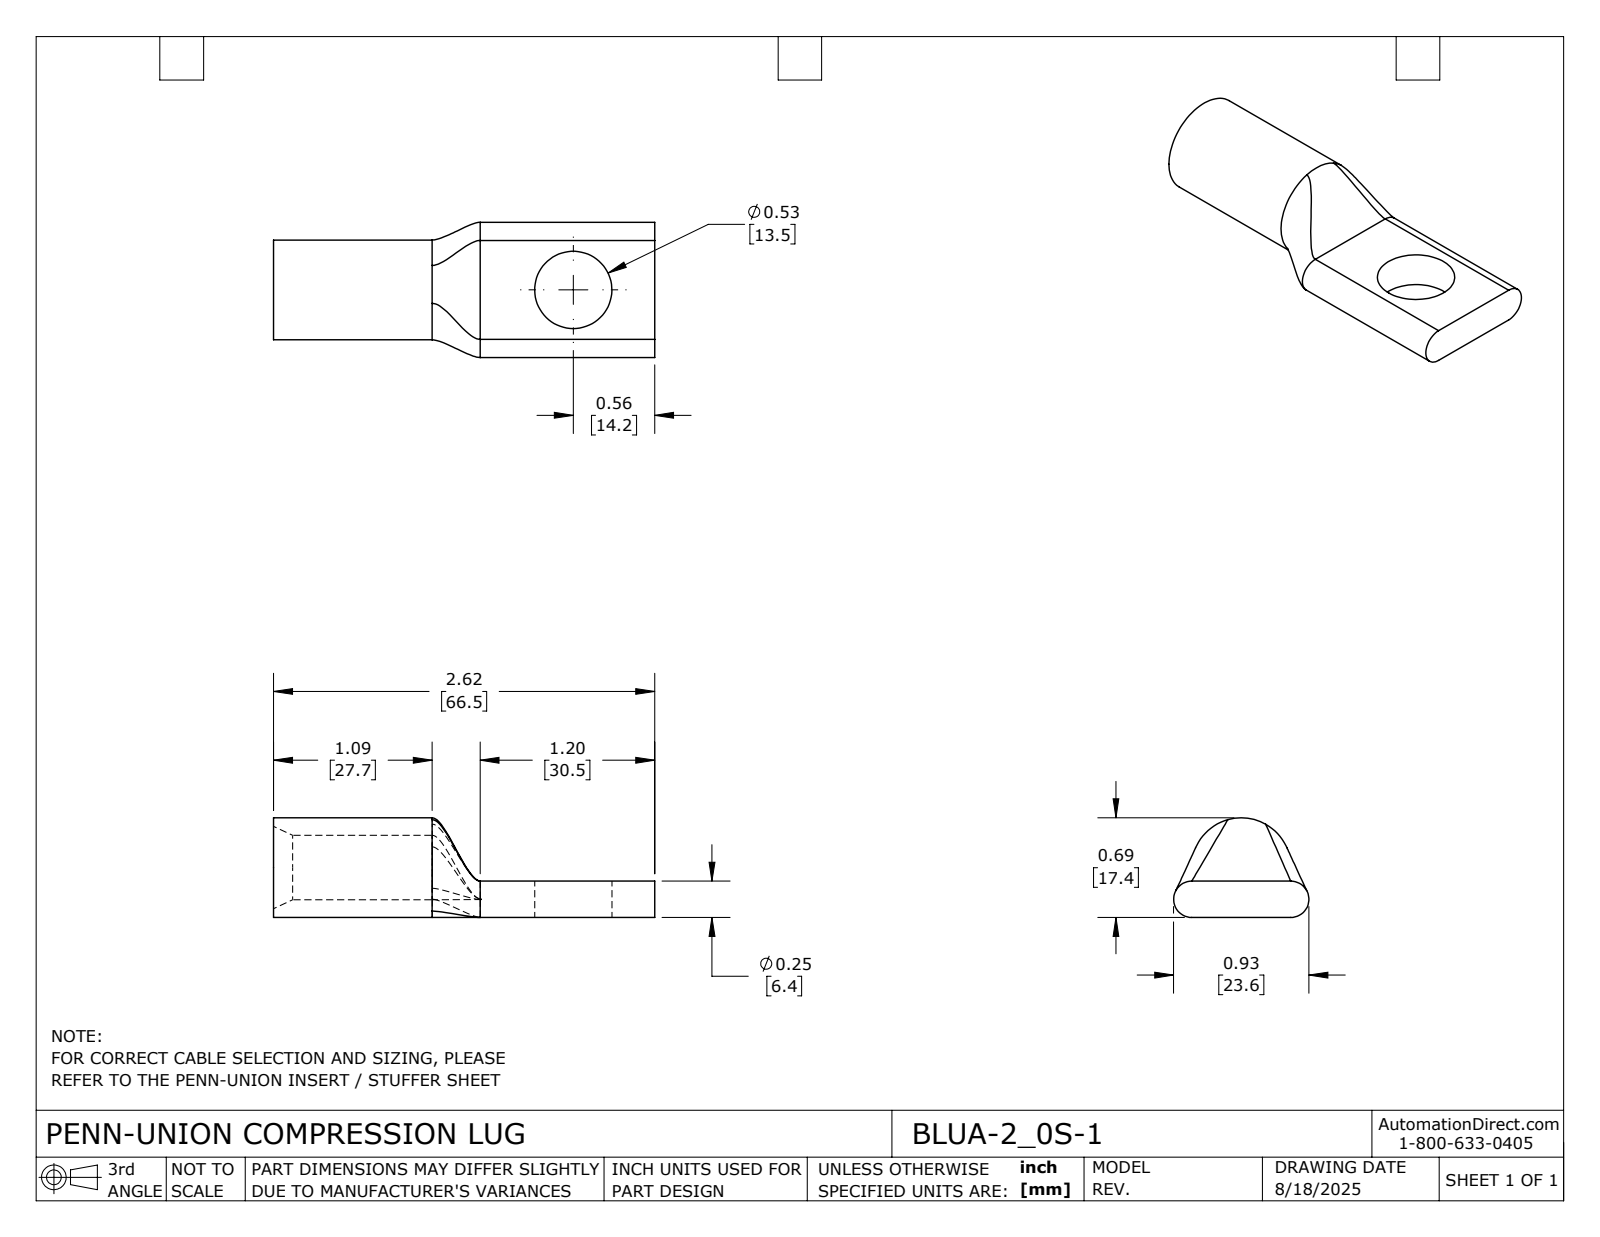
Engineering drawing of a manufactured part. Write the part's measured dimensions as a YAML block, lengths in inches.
part_name: "BLUA-2_0S-1"
step_written_by: "SolidWorks 2024 (CONFIG_CONTROL_DESIGN)"
units: inches
bodies: {solids: 1, faces: 24, planar: 5, cylindrical: 9, other: 10}
overall_size: [2.62, 0.93, 0.685]
volume: 0.506
surface_area: 8.21
round_holes:
  - {diameter: 0.443, count: 1}
  - {diameter: 0.531, count: 1}
round_bosses_or_shafts:
  - {diameter: 0.685, count: 1}
partial_cylinders:
  - {radius: 0.125, count: 2}
face_to_face_distances: [0.25, 2.62, 1.42, 1.2]
